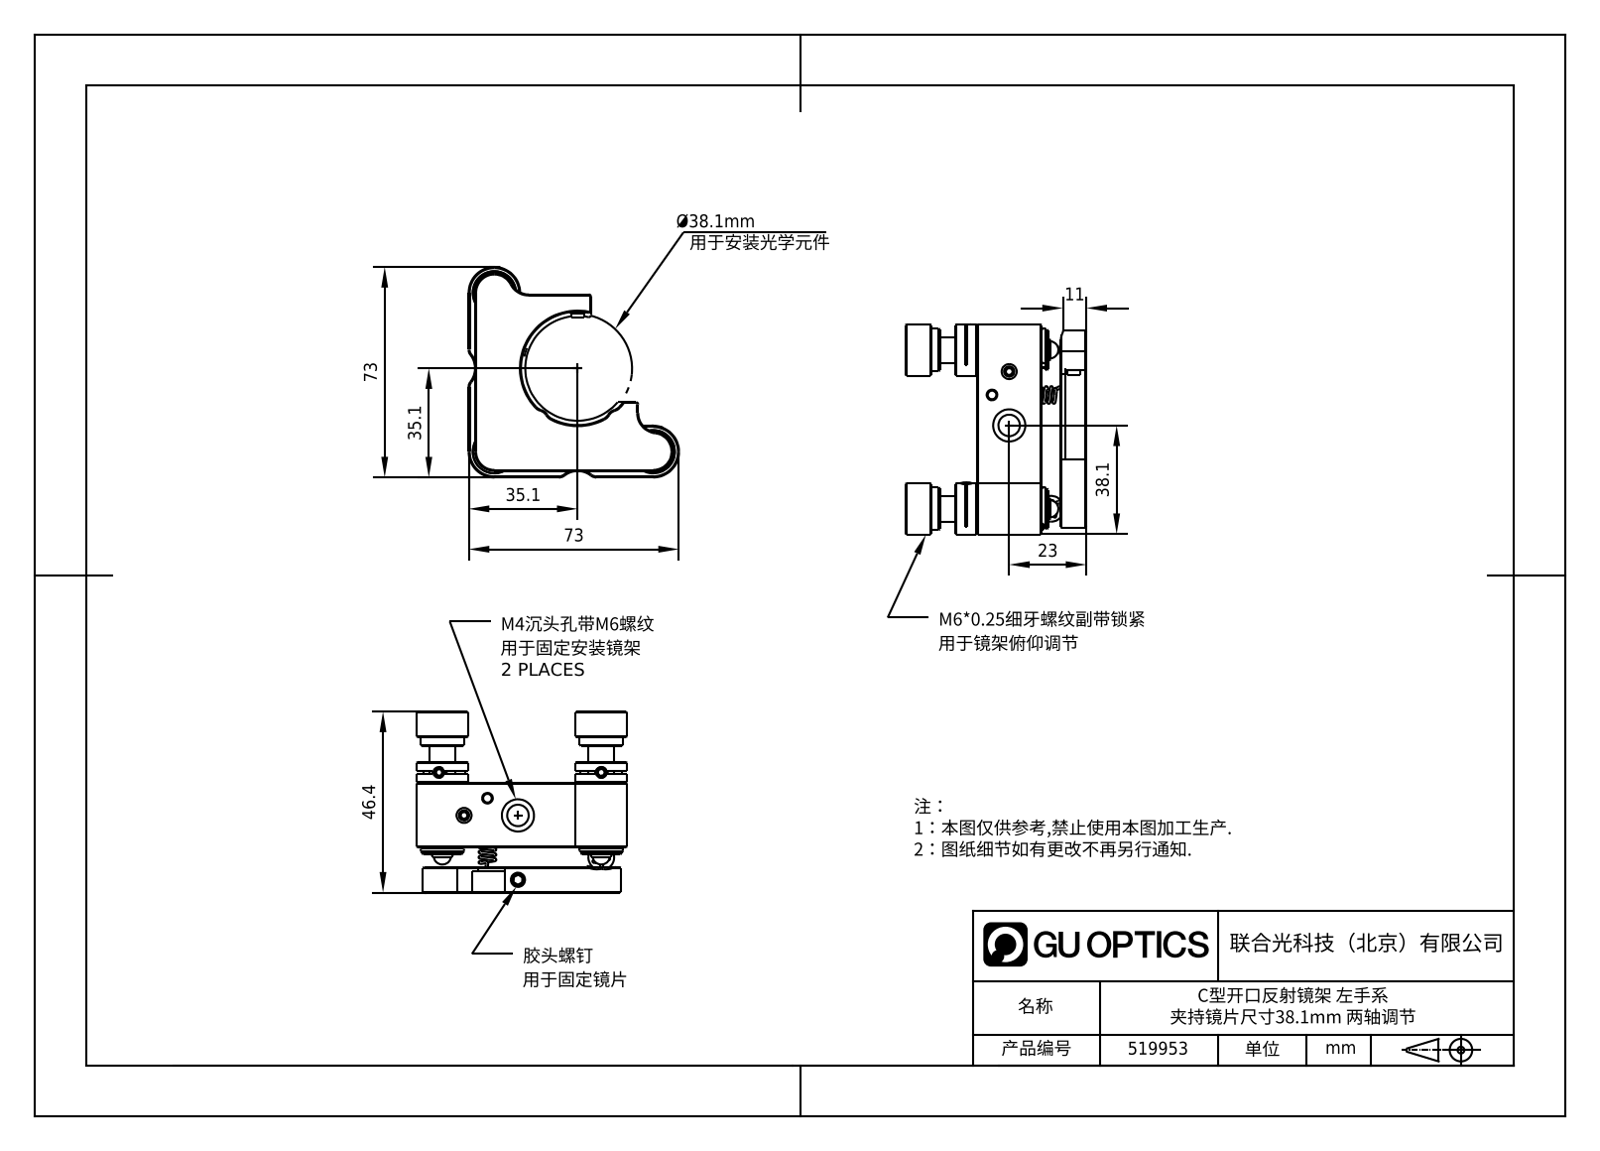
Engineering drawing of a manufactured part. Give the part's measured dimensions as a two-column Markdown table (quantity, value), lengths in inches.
| quantity | value |
| --- | --- |
| STEP written by | SolidWorks 2021 (CONFIG_CONTROL_DESIGN) |
| units | inches |
| bodies | 0 solids, 458 faces (153 planar, 147 cylindrical, 158 other) |
| overall size | 2.874 × 2.874 × 1.808 |
| round holes (diameter × count) | 0.098 × 10, 0.236 × 4, 0.157 × 2, 0.197 × 2, 0.295 × 2, 0.13 × 1, 0.374 × 1 |
| round bosses / shafts (diameter × count) | 0.118 × 6, 0.394 × 3, 0.472 × 2, 0.374 × 2, 0.315 × 2, 0.236 × 2, 0.157 × 2 |
| partial cylindrical surfaces (radius × count) | 0.079 × 9, 0.008 × 5, 0.02 × 5, 0.177 × 3, 0.394 × 3, 0.098 × 2, 0.197 × 2, 0.236 × 2 |
| main face-to-face distances | 0.472, 0.059, 0.157, 1.22, 0.748, 0.63, 0.591, 0.413, 0.039, 0.089 |
| hole center spacings | 1.22, 0.591, 0.98, 1.811, 0.426, 0.626, 0.867, 0.905 |
